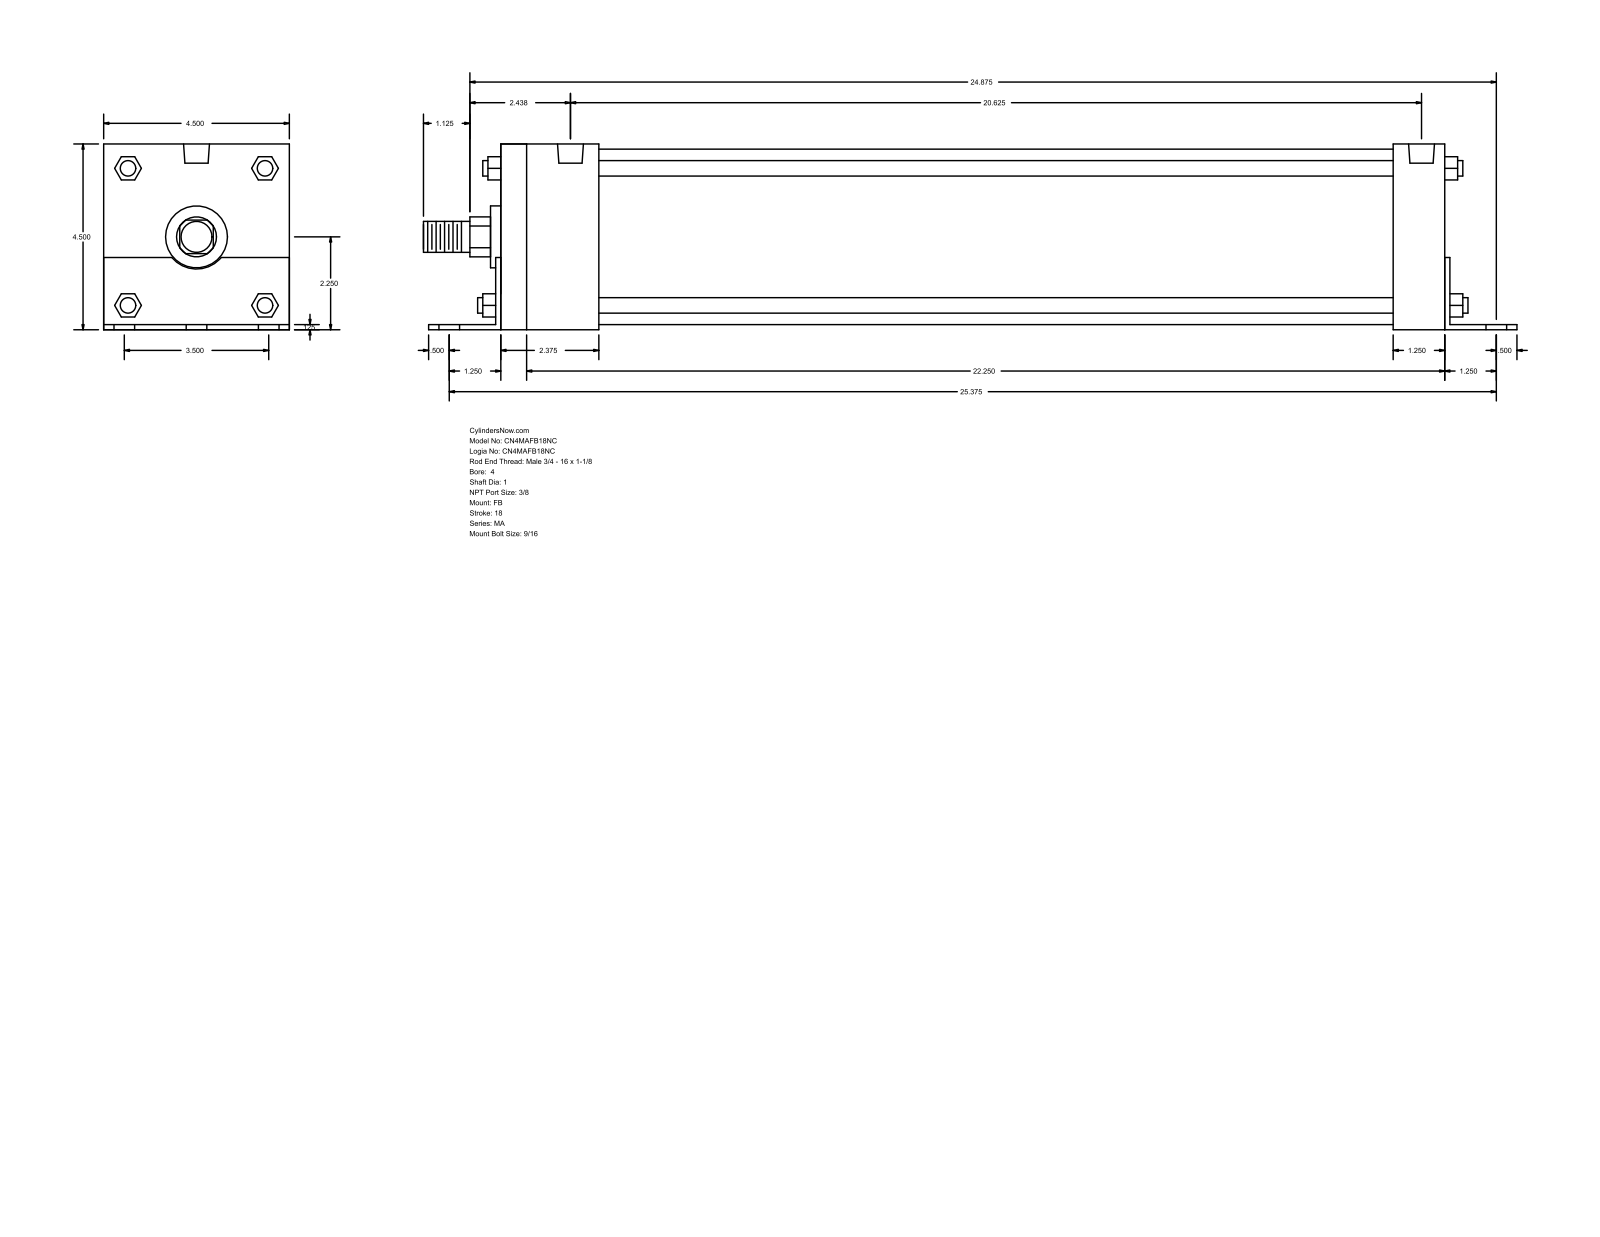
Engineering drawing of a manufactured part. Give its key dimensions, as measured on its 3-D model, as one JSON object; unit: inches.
{"part_name": "MA_FB__0400_1", "step_written_by": "GSSL Pune (CONFIG_CONTROL_DESIGN)", "units": "inches", "bodies": {"solids": 0, "faces": 140, "planar": 105, "cylindrical": 35, "other": 0}, "overall_size": [26.5, 4.502, 4.5], "round_holes": [[0.563, 6], [0.437, 4], [0.627, 2]], "round_bosses_or_shafts": [[0.375, 4], [4.25, 1], [1.5, 1], [1, 1], [0.75, 1]], "partial_cylinders_radius": [[0.484, 1], [0.78, 1]], "face_to_face_distances": [4.5, 0.125, 4.502, 23, 0.123, 4.377, 22.875, 23.125, 21.75, 21.625], "hole_center_spacings": [1.75, 25.435, 25.375, 2.52, 2.658, 3.419, 3.5, 3.581]}
